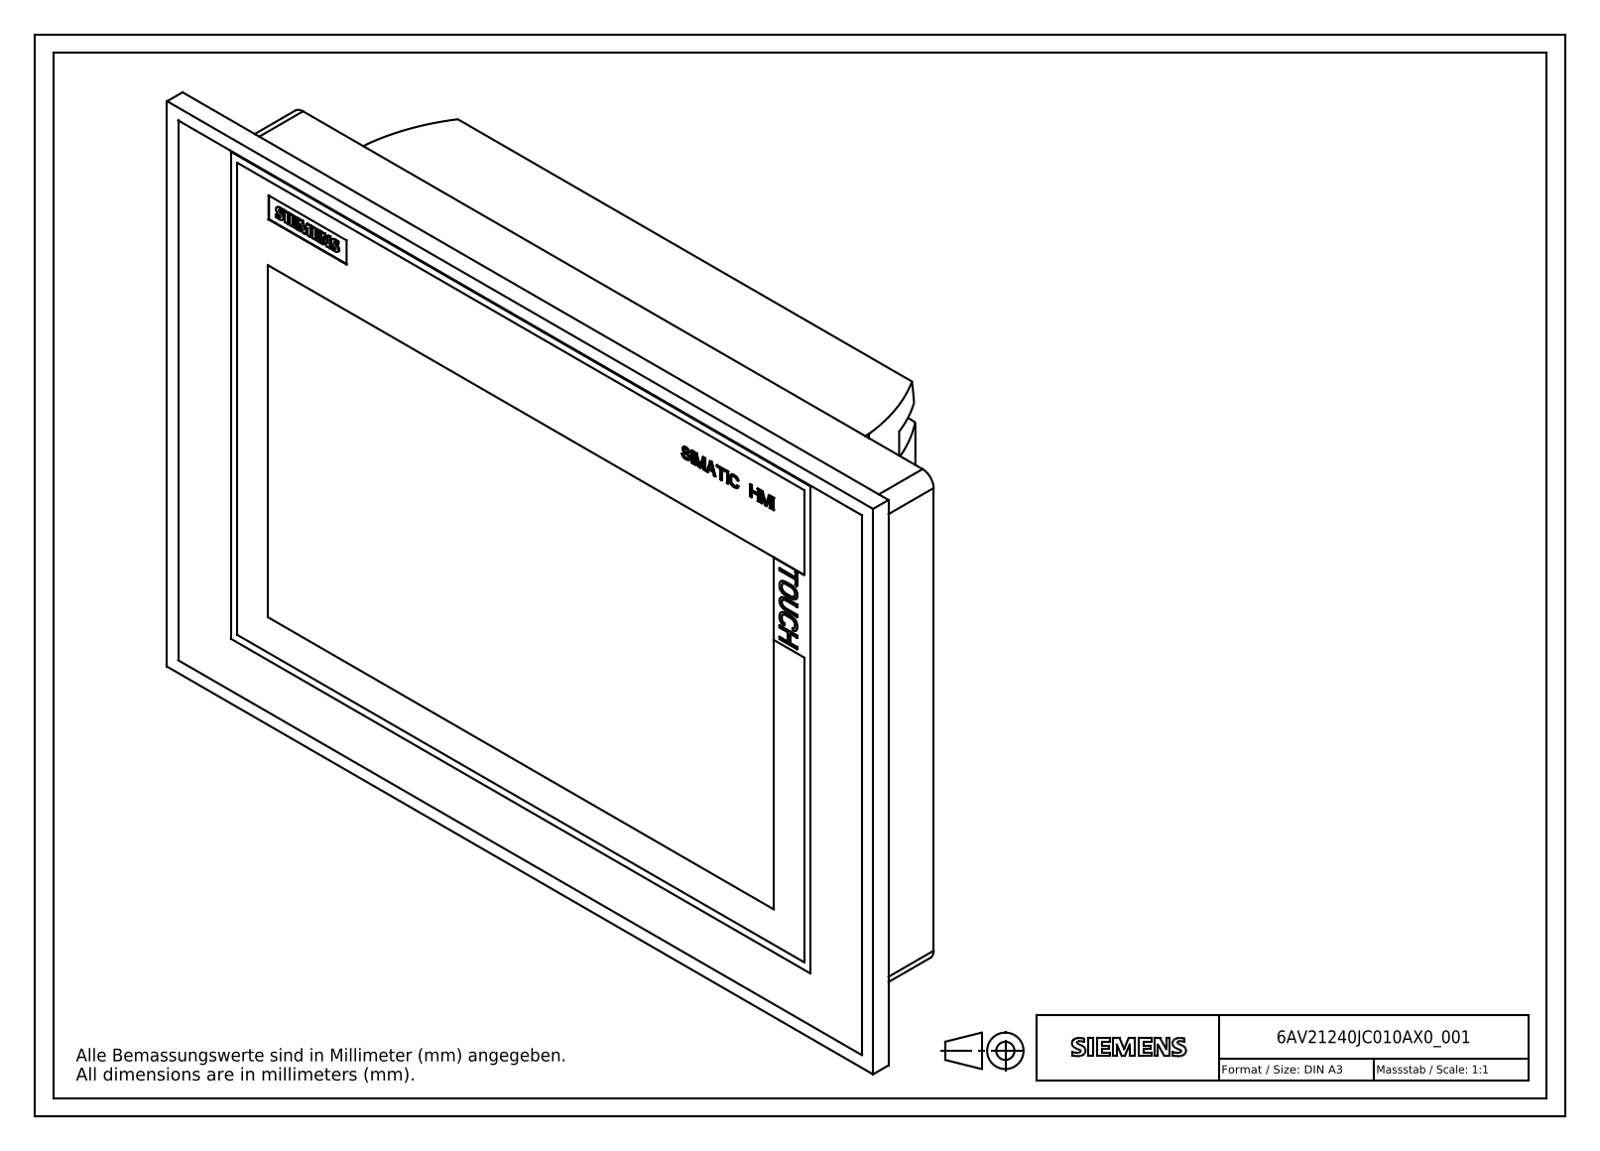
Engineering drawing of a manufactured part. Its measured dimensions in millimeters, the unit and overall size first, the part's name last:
Units: millimetres
Overall size (bounding box): 274 × 190 × 68.8
Round holes (diameter × count): ⌀0.9 ×9, ⌀2.4 ×2, ⌀3.8 ×2, ⌀8.5 ×2
Round bosses / shafts (diameter × count): ⌀5.5 ×5, ⌀7 ×3, ⌀6 ×3, ⌀3 ×2, ⌀0.96 ×2, ⌀0.8 ×2
Partial cylindrical surfaces — rounded edges, fillets, slot ends (radius × count): R0.2 ×77, R1 ×18, R0.85 ×6, R3 ×6, R0.45 ×4, R1.85 ×4, R2.02 ×4, R3.75 ×4
Main face-to-face distances: 5.02, 62.7, 67.72, 68.5, 5.8, 0.78, 0.66, 5.68, 68.38, 32.7
Hole centre spacings: 3.07, 2.76, 4.96, 5.52, 7.42, 8.28, 7.15, 8.44
Volume: 2 213 000 mm³ · Surface area: 278 937 mm²
Bodies: 265 solids, 2801 faces (2315 planar, 206 cylindrical, 280 other)
Part name (STEP PRODUCT): A5E30321192A_001; A5E30291703A_001; A5E30291702A_001; A5E30291699A_001 (+1 more)
STEP written by: SIEMENS UGS NX 6.0 (AUTOMOTIVE_DESIGN)
